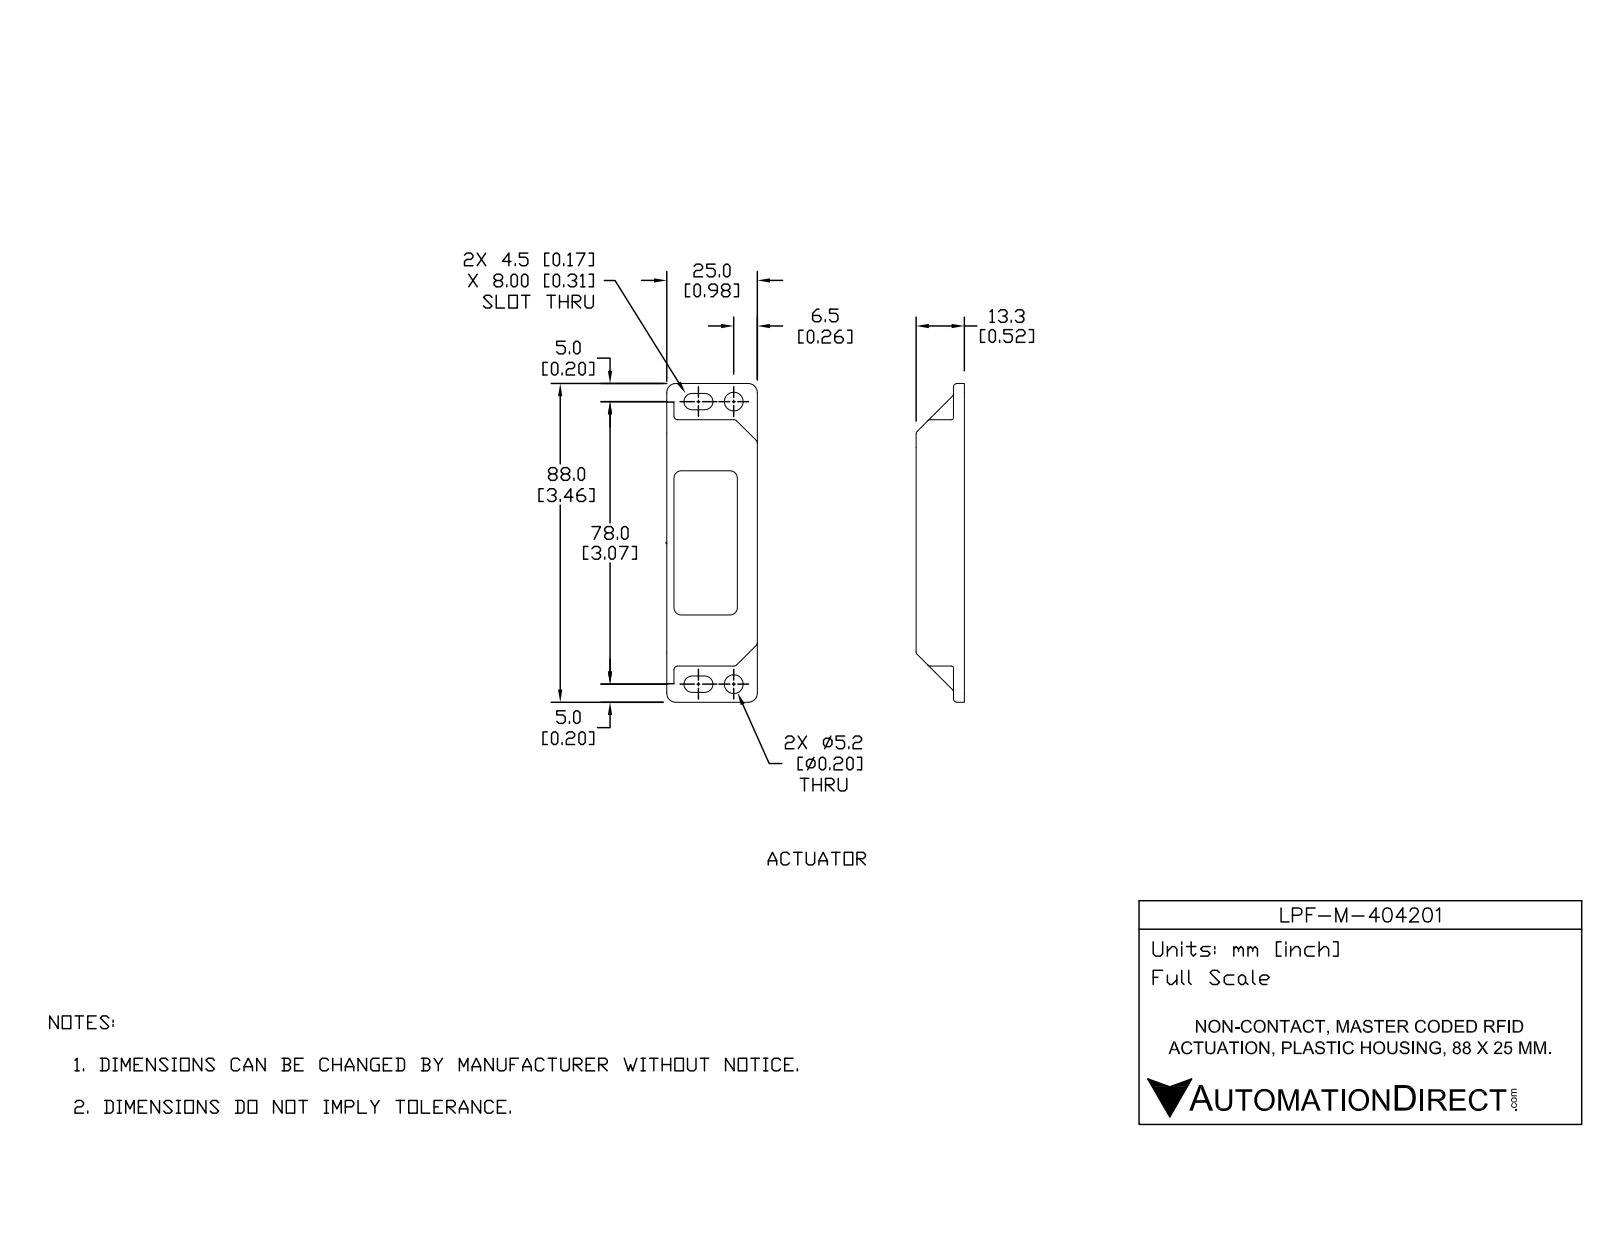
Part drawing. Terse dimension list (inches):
name: LPF-M-404201
written by: SolidWorks 2017 (AUTOMOTIVE_DESIGN)
unit: in
bodies: 4 solids, 432 faces (179 planar, 120 cylindrical, 133 other)
size: 3.465 × 0.996 × 0.524
volume: 0.623 in³; area: 19.4 in²
holes: 2× ⌀0.197, 2× ⌀0.205
bosses: 2× ⌀0.193, 2× ⌀0.079
rounds: 61× R0.02, 26× R0.039, 6× R0.079, 4× R0.089, 4× R0.098
face distances: 0.067, 0.441, 0.079, 0.374, 0.059, 0.071, 0.508, 0.445, 0.512, 0.984
hole spacings: 1.19, 1.895, 0.709, 3.071
